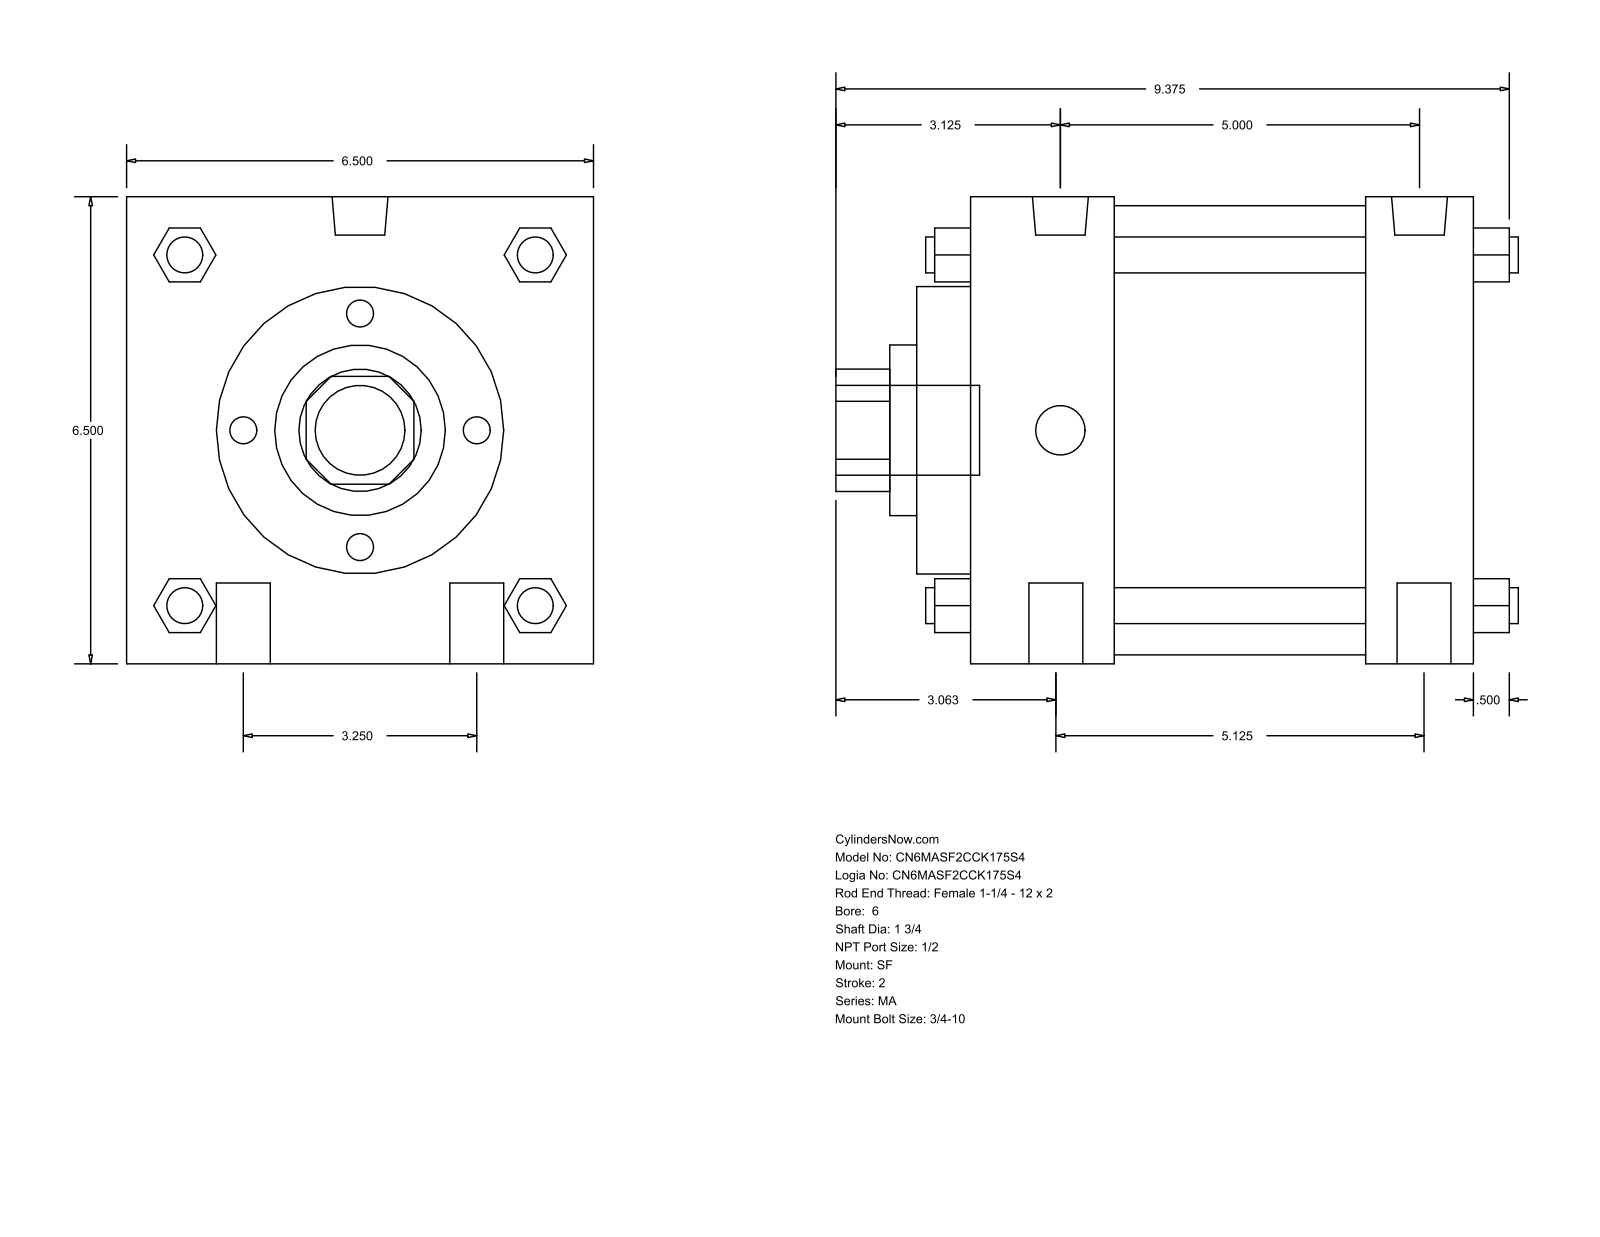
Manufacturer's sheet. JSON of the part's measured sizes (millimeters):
{"part_name": "MA_SF__0600_1.75", "step_written_by": "GSSL Pune (CONFIG_CONTROL_DESIGN)", "units": "millimeters", "bodies": {"solids": 0, "faces": 126, "planar": 95, "cylindrical": 31, "other": 0}, "overall_size": [241.3, 165.1, 165.1], "round_holes": [[44.45, 1], [60.33, 1], [101.6, 1], [158.75, 1]], "round_bosses_or_shafts": [[19.05, 4], [12.7, 4], [19.77, 2], [17.46, 2], [31.75, 1]], "partial_cylinders_radius": [[21.63, 1]], "face_to_face_distances": [165.1, 177.81, 19.05, 50.8, 139.7, 88.9, 38.11, 127.01, 69.85, 158.75]}
